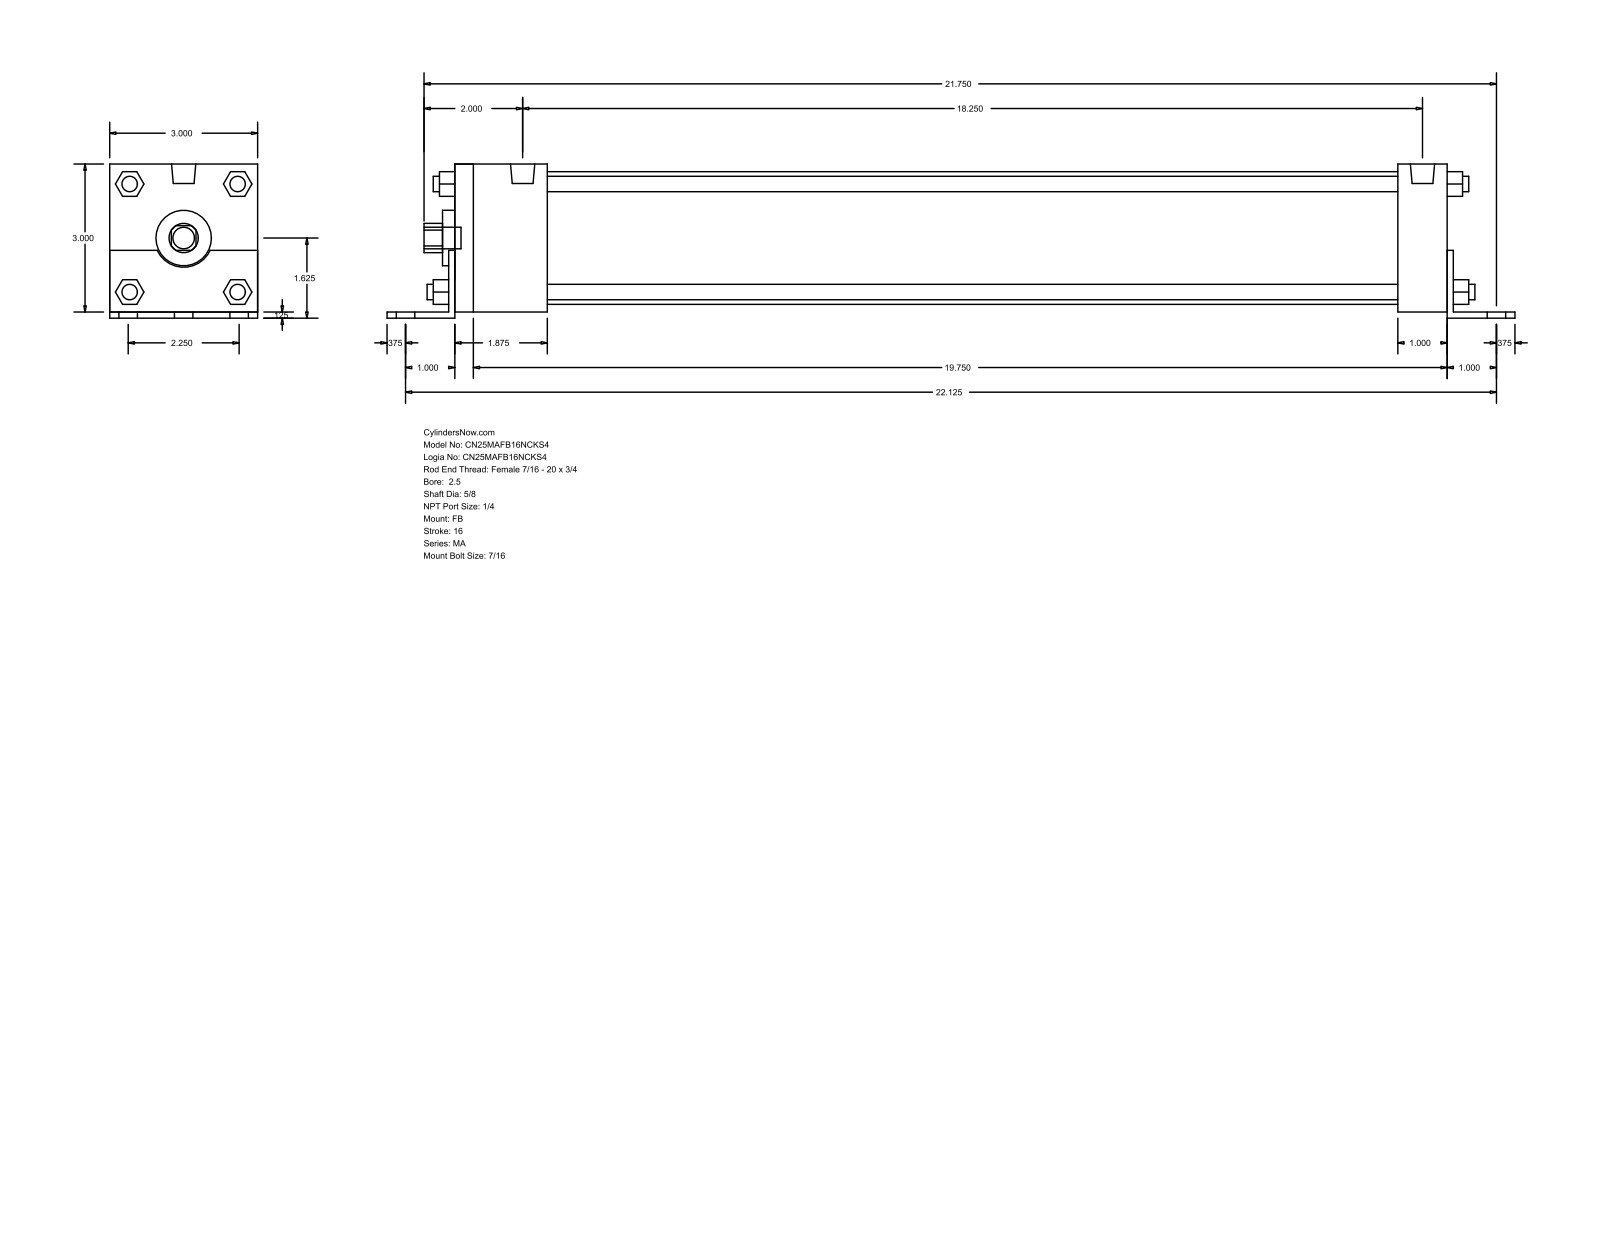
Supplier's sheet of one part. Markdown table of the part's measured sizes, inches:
| quantity | value |
| --- | --- |
| part name | MA_FB__0250_0.625 |
| STEP written by | GSSL Pune (CONFIG_CONTROL_DESIGN) |
| units | inches |
| bodies | 0 solids, 140 faces (105 planar, 35 cylindrical, 0 other) |
| overall size | 22.875 × 3.125 × 3 |
| round holes (diameter × count) | 0.625 × 1, 1.125 × 1, 2.69 × 1 |
| round bosses / shafts (diameter × count) | 0.313 × 8, 0.437 × 7, 0.492 × 2 |
| partial cylindrical surfaces (radius × count) | 0.297 × 1, 0.593 × 1 |
| main face-to-face distances | 3, 0.125, 3.125, 0.125, 20.25, 20.125, 1.125, 1.875, 1, 20.375 |
